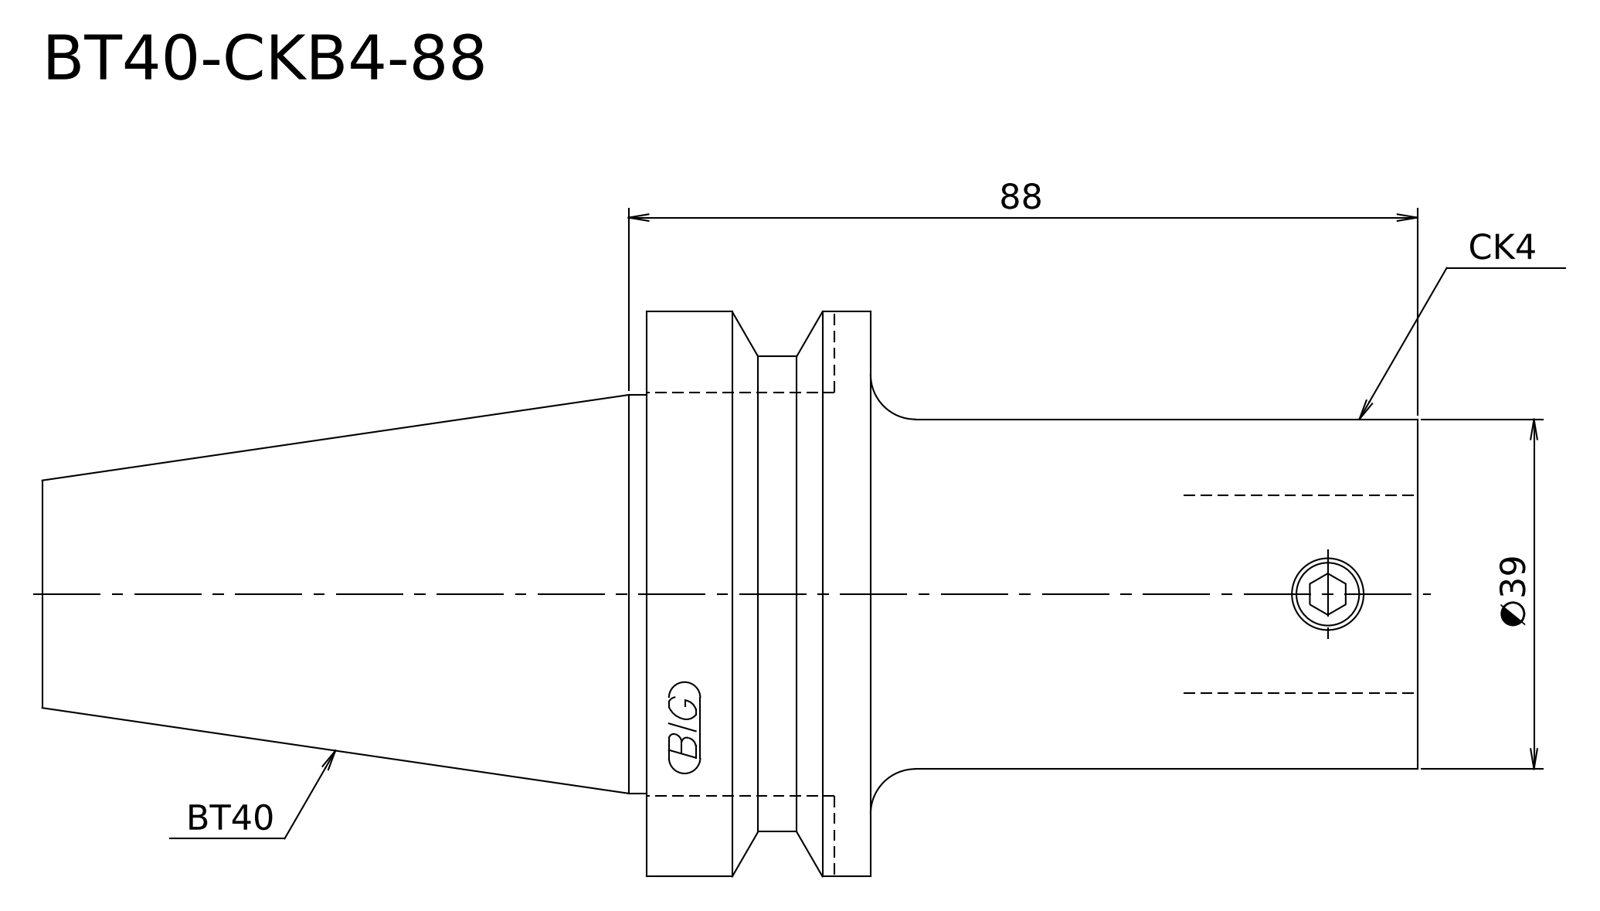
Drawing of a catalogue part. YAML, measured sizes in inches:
step_written_by: "Kubotek KeyCreator V8.5.1 (14335) (CONFIG_CONTROL_DESIGN)"
units: inches
bodies: {solids: 1, faces: 14, planar: 4, cylindrical: 5, other: 5}
overall_size: [6.039, 2.48, 2.48]
volume: 13.01
surface_area: 39.66
round_bosses_or_shafts:
  - {diameter: 2.48, count: 1}
  - {diameter: 2.087, count: 1}
  - {diameter: 1.75, count: 1}
  - {diameter: 1.535, count: 1}
face_to_face_distances: [0.984, 2.402, 3.386, 6.039, 3.638, 2.654]
